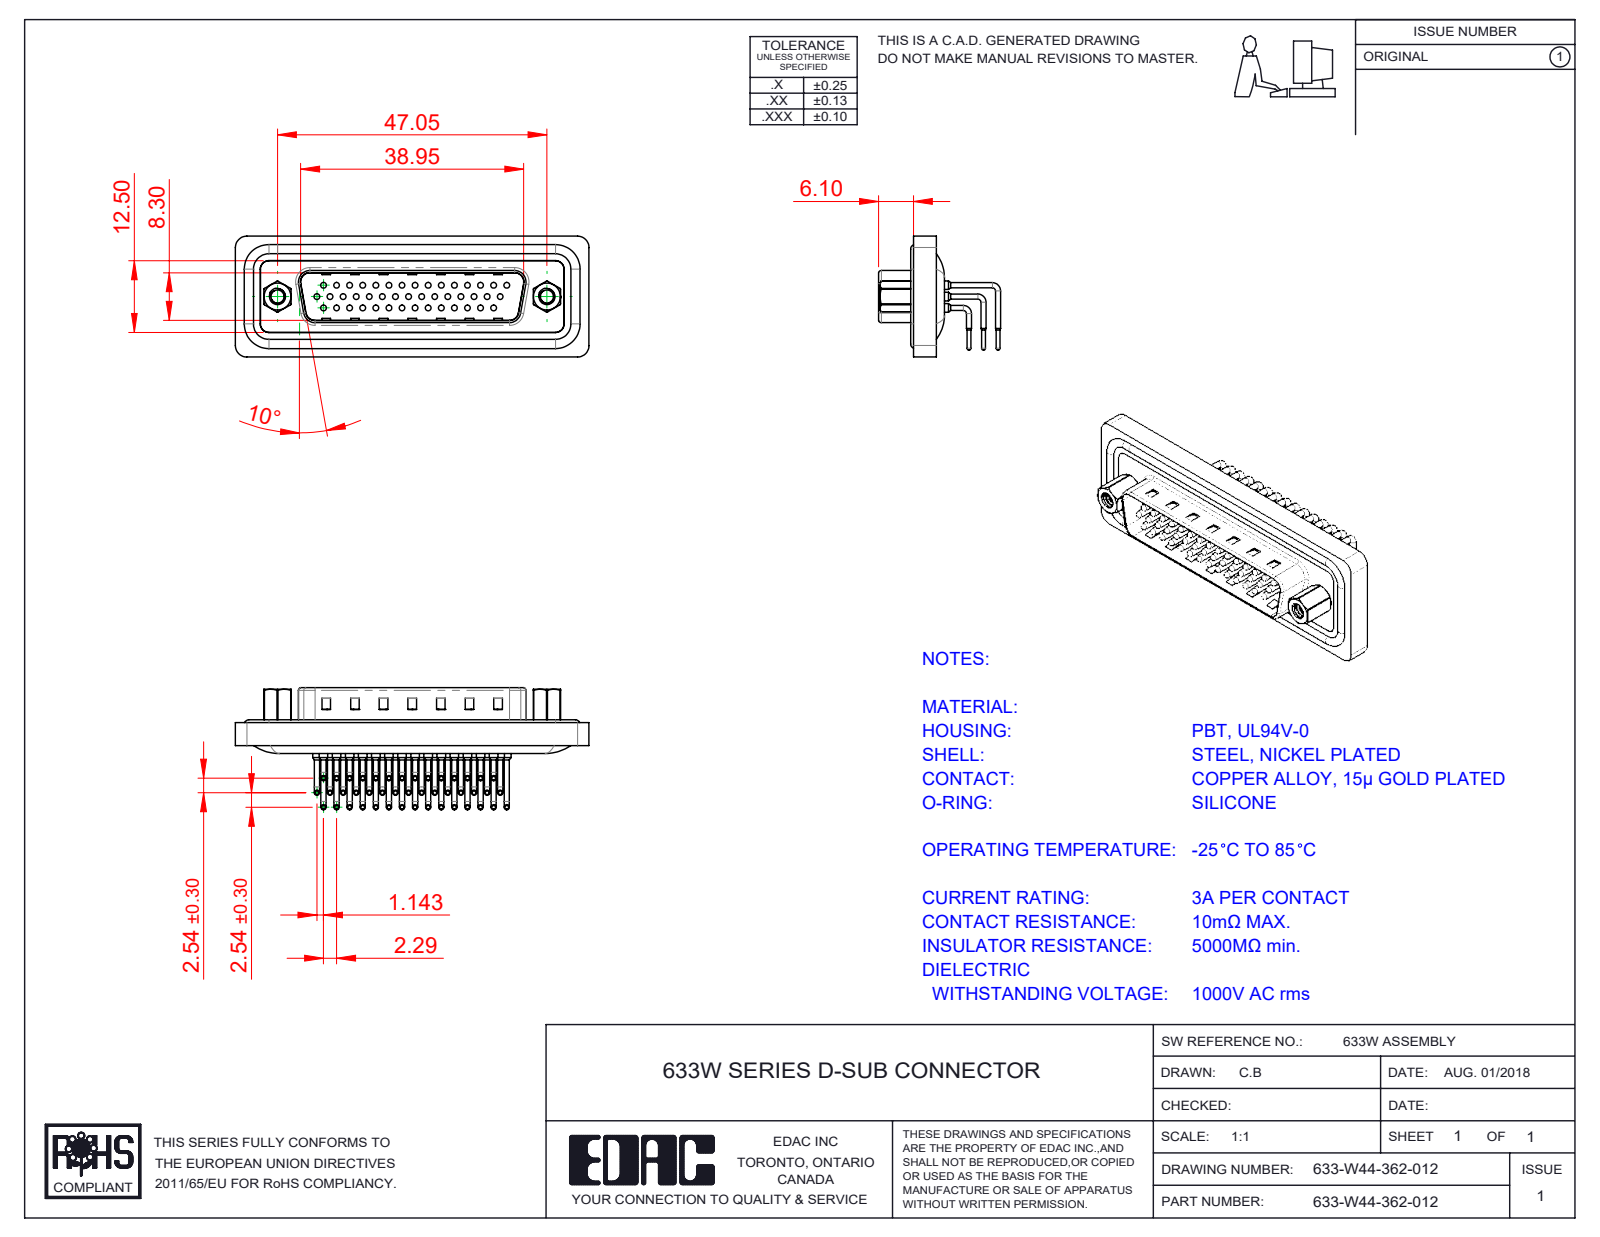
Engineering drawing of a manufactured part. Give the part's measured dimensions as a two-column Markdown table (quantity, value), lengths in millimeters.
| quantity | value |
| --- | --- |
| part name | 633W Housing_44 Contacts; 633W Waterproof Housing_44 Contacts; 633W Contact Row 2; 633W 4-40 Hex Standoff (+5 more) |
| STEP written by | SolidWorks 2016 (CONFIG_CONTROL_DESIGN) |
| units | millimeters |
| bodies | 52 solids, 5438 faces (3021 planar, 1882 cylindrical, 535 other) |
| overall size | 61.74 × 21.32 × 21.1 |
| volume | 6 688 mm³ |
| surface area | 13 603 mm² |
| round holes (diameter × count) | 1 × 44, 1.5 × 44, 1.7 × 44, 2 × 44, 2.26 × 2, 2.29 × 2, 4 × 2, 4.8 × 2, 5 × 2 |
| round bosses / shafts (diameter × count) | 0.9 × 88, 0.65 × 44, 1.5 × 18, 1.6 × 4, 4.9 × 2, 2.79 × 2, 5 × 1 |
| partial cylindrical surfaces (radius × count) | 1.01 × 44, 2 × 14, 1.5 × 13, 0.5 × 8, 2.7 × 6, 0.9 × 4, 1.6 × 4, 4.3 × 4 |
| main face-to-face distances | 0.4, 1.6, 2.5, 2.9, 1.1, 5.65, 15.45, 0.75, 14.7, 6.4 |
| hole center spacings | 2.28, 3.96, 2.29, 4.57, 8.24, 6.86, 11.43, 14.99 |
